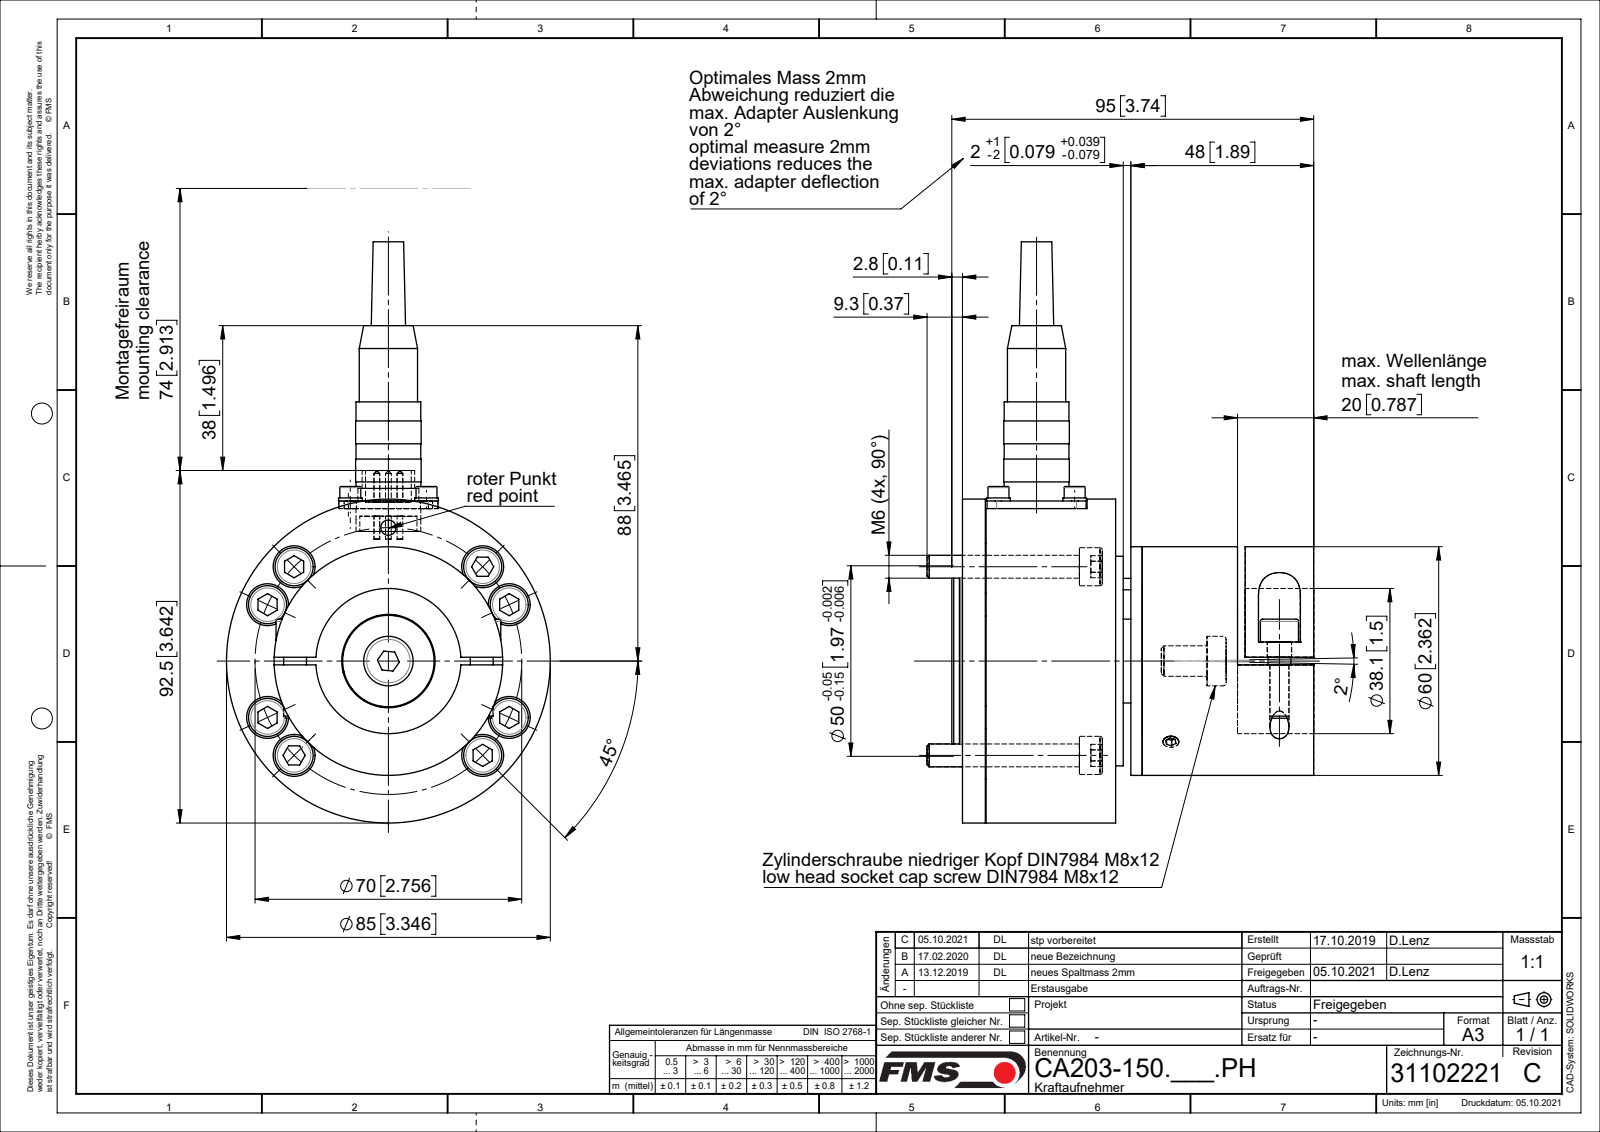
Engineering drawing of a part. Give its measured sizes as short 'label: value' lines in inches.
name: Sch DIN9021_M8; 061205-3_01; Kabeldose_M14x1_Mini_5pol; 070907-4_01 (+8 more)
written by: SolidWorks 2018 (CONFIG_CONTROL_DESIGN)
unit: in
bodies: 44 solids, 821 faces (294 planar, 332 cylindrical, 195 other)
size: 6.004 × 3.996 × 3.346
volume: 17.73 in³; area: 169.7 in²
holes: 8× ⌀0.098, 8× ⌀0.256, 8× ⌀0.433, 6× ⌀0.197, 5× ⌀0.157, 4× ⌀0.122, 4× ⌀0.126, 4× ⌀0.142, 4× ⌀0.276, 2× ⌀0.252, 1× ⌀0.118, 1× ⌀0.165
bosses: 11× ⌀0.236, 10× ⌀0.394, 8× ⌀0.118, 5× ⌀0.059, 4× ⌀0.244, 4× ⌀0.224, 4× ⌀0.217, 1× ⌀3.346
rounds: 4× R0.098, 2× R0.197, 2× R0.217
face distances: 0.079, 1.181, 1.614, 0.236, 0.394, 1.772, 0.118, 1.969, 1.339, 0.787
hole spacings: 1.378, 0.787, 0.976, 0.992, 1.291, 2.013, 2.223, 1.113
